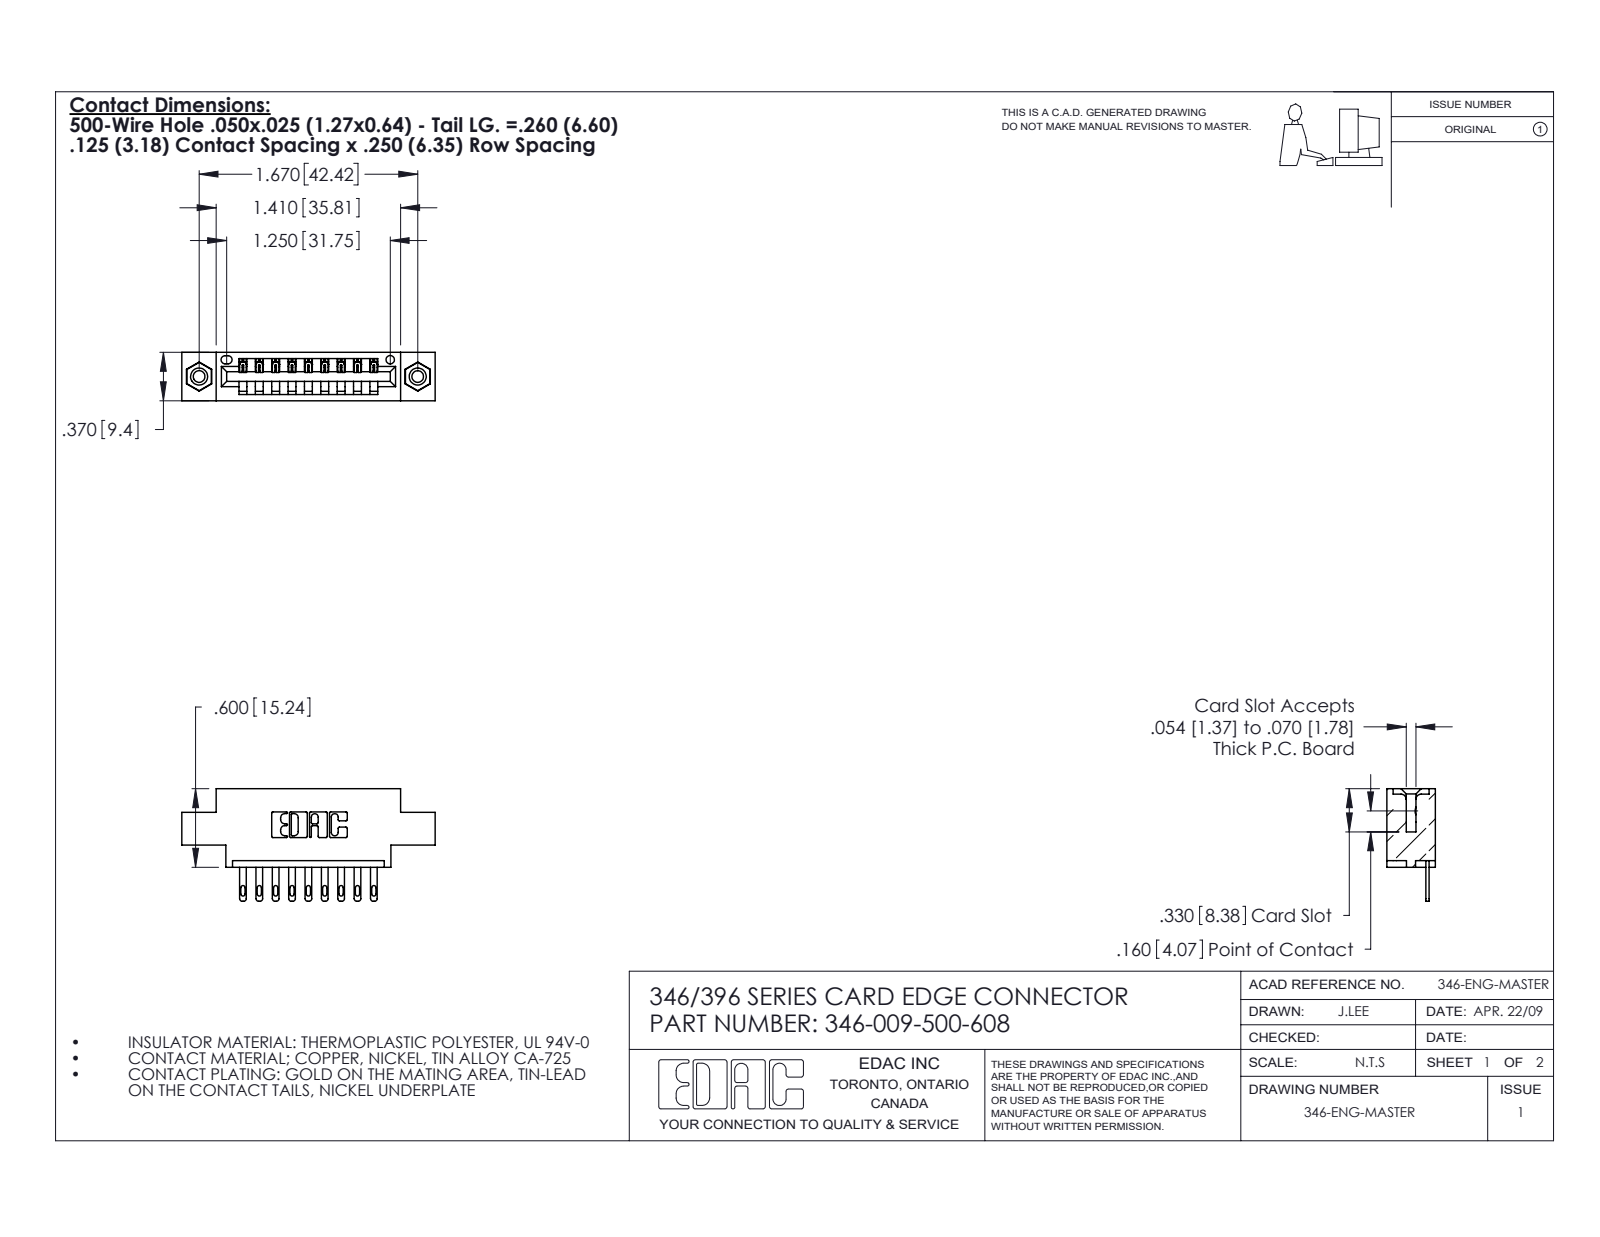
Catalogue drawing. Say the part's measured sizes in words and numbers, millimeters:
The part is named "345-292-001_345-293-100; 346 Part_0.170 Offset - 0.156 Dia-TI; 345-250-001_345-250-003-102; 346-009-500-608". Its 3-D file was written by "SolidWorks 2020 (CONFIG_CONTROL_DESIGN)". It is 12 solids with 672 faces: 418 planar, 238 cylindrical and 16 other. Overall it measures 49.1 by 21.8 by 9.4 millimeters. Its volume is 4 330 cubic millimeters and its surface area 5 248 square millimeters. Round holes: 2 of diameter 2.3, 2 of diameter 3.2, 2 of diameter 4, 1 of diameter 1.6. Round bosses or shafts: 2 of diameter 3.9. Partial cylindrical surfaces (rounded edges, fillets, slot ends): 22 of radius 0.3, 18 of radius 0.2, 18 of radius 0.4, 18 of radius 0.5, 6 of radius 0.2, 6 of radius 0.8, 3 of radius 0.7, 2 of radius 0.8. The main face-to-face distances are 6.4, 9.4, 1.2, 8.2, 1.8, 7.6, 0.6, 5.6, 3.8, 2.5. The hole center spacings are 6.2, 37.2, 42.4.
